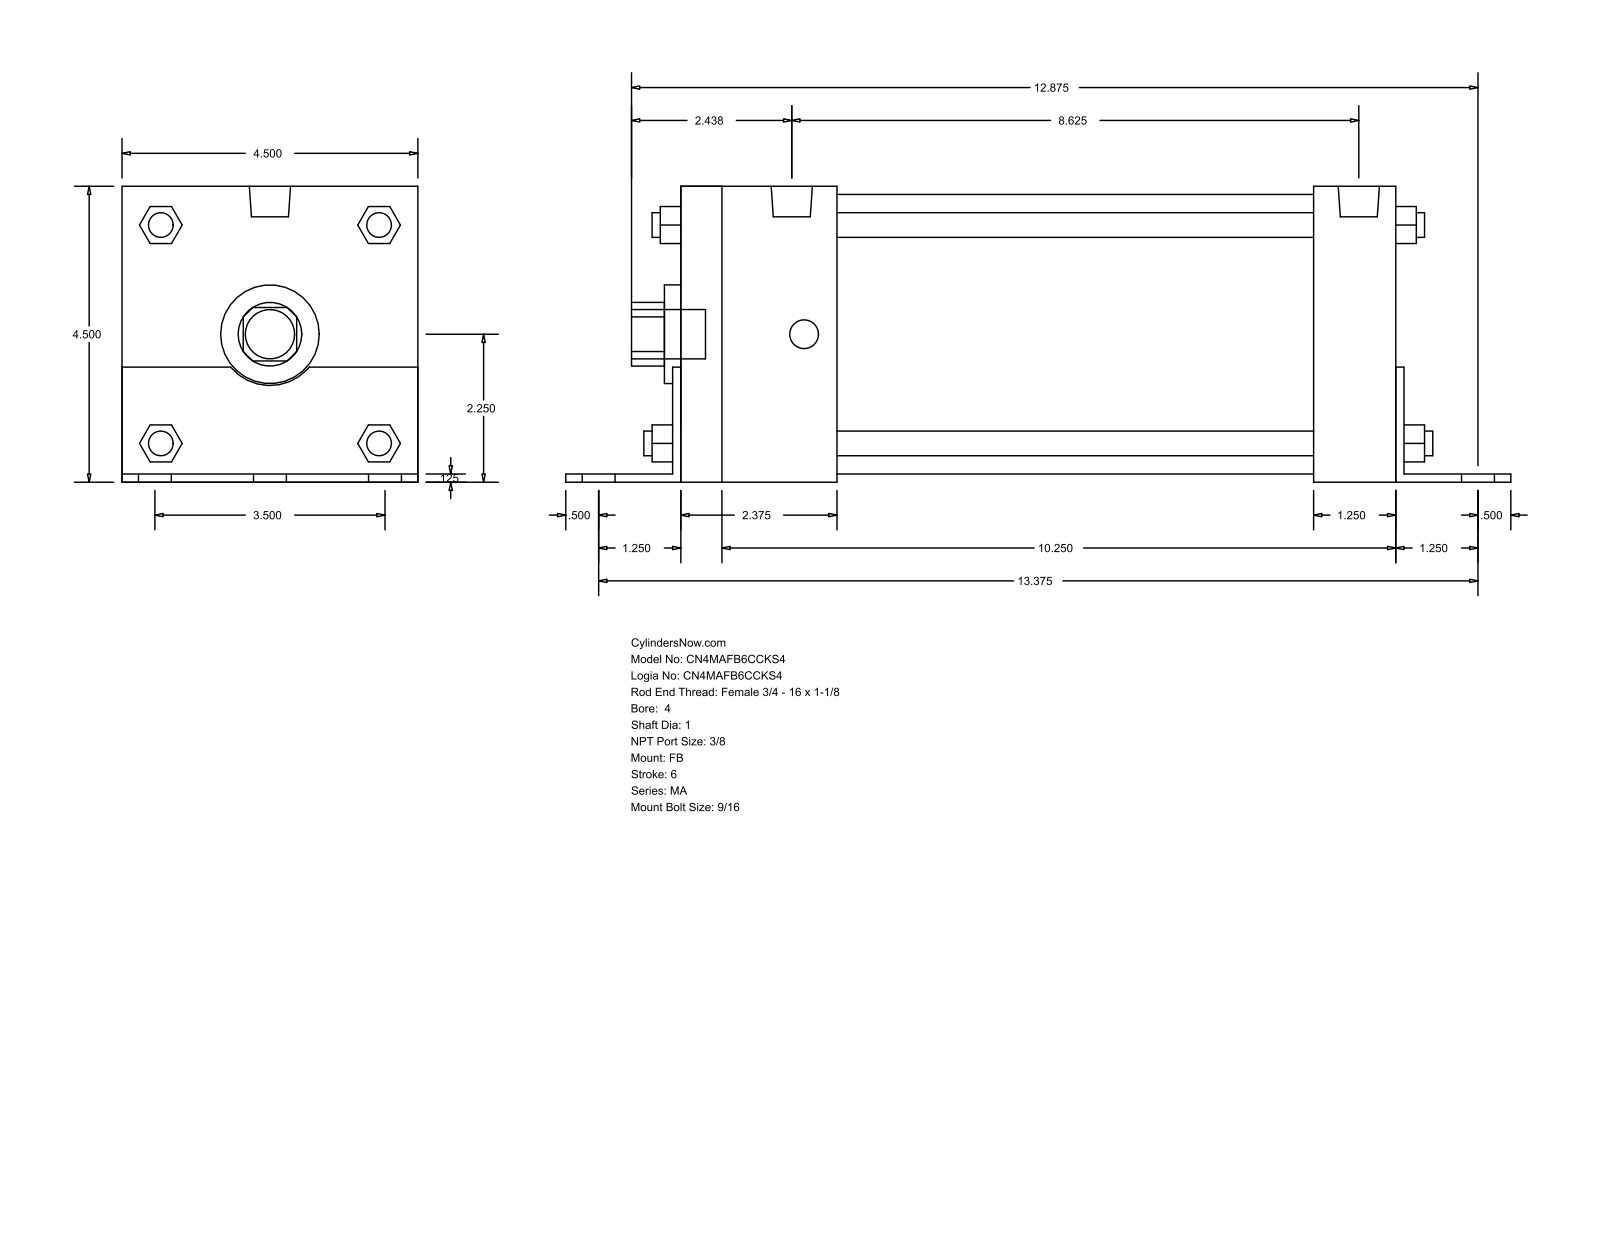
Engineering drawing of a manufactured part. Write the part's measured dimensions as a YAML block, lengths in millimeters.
part_name: "MA_FB__0400_1"
step_written_by: "GSSL Pune (CONFIG_CONTROL_DESIGN)"
units: millimeters
bodies: {solids: 0, faces: 140, planar: 105, cylindrical: 35, other: 0}
overall_size: [365.12, 114.35, 114.3]
round_holes:
  - {diameter: 25.4, count: 1}
  - {diameter: 38.1, count: 1}
  - {diameter: 107.95, count: 1}
round_bosses_or_shafts:
  - {diameter: 14.29, count: 6}
  - {diameter: 11.11, count: 4}
  - {diameter: 9.53, count: 4}
  - {diameter: 15.93, count: 2}
  - {diameter: 19.05, count: 1}
partial_cylinders:
  - {radius: 12.29, count: 1}
  - {radius: 19.81, count: 1}
face_to_face_distances: [114.3, 3.17, 114.35, 3.12, 111.18, 276.22, 3.18, 282.57, 279.4, 279.39]
